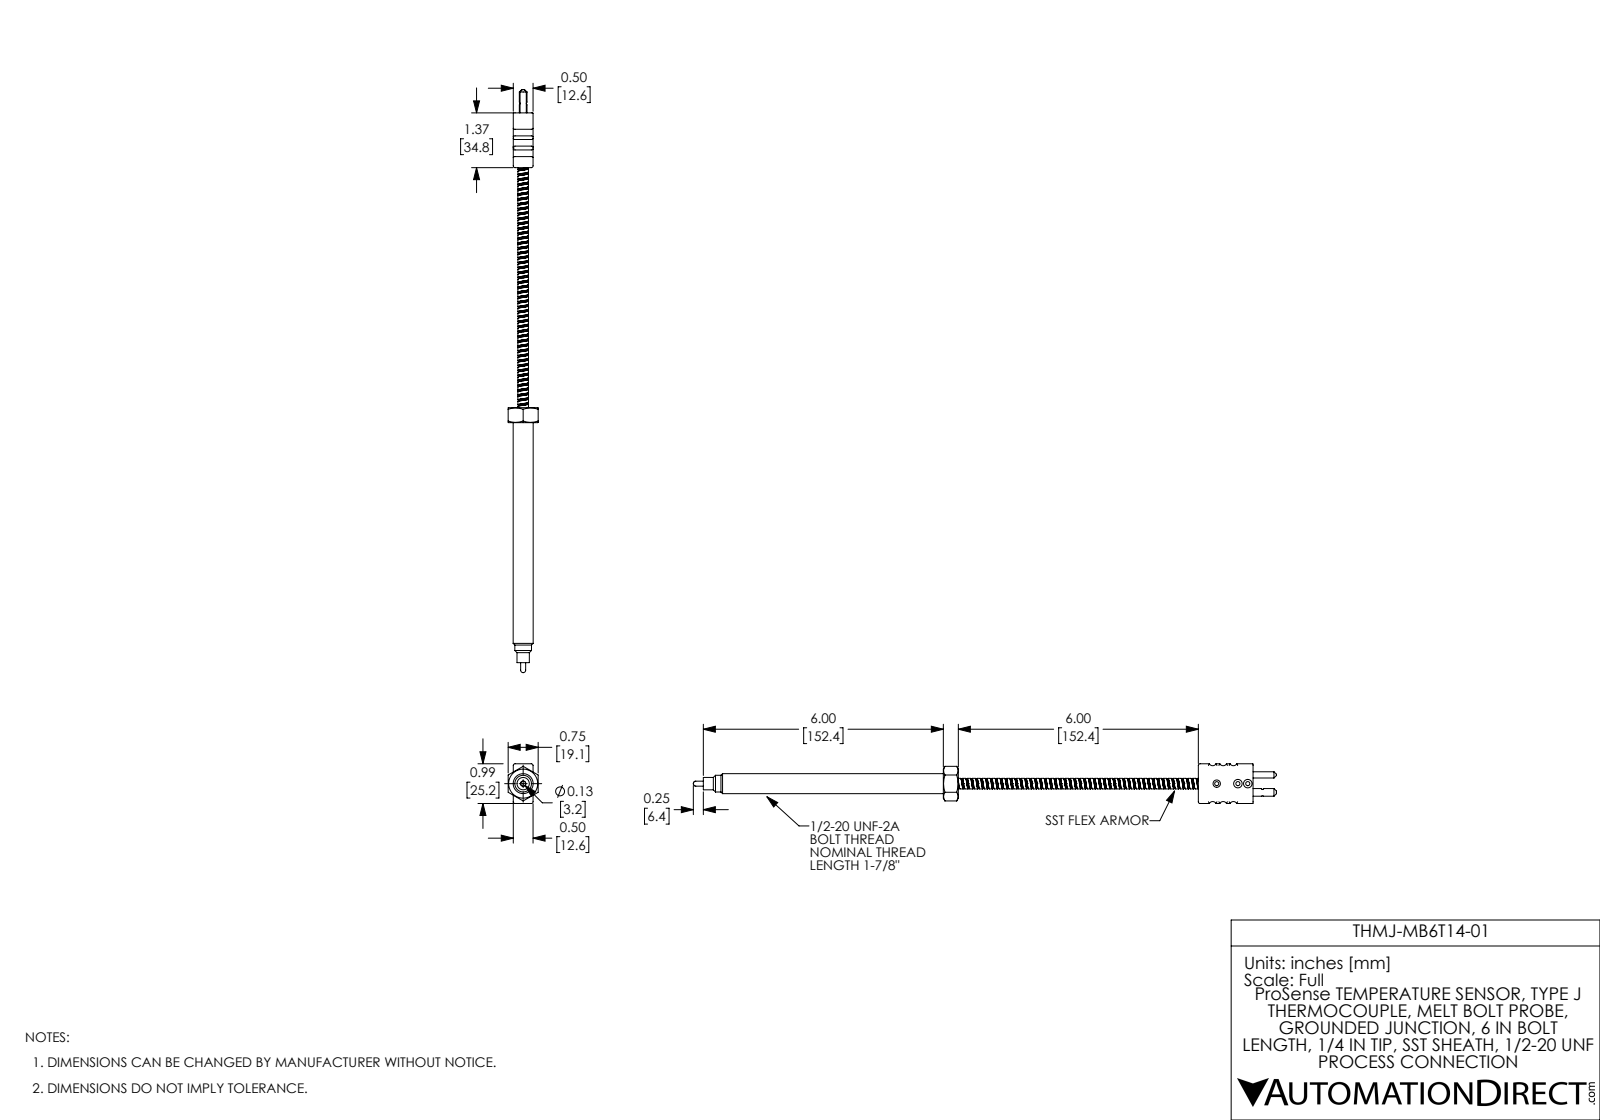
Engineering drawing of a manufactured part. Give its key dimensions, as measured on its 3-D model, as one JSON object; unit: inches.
{"part_name": "THMJ-MB6T14-01", "step_written_by": "SolidWorks 2017 (AUTOMOTIVE_DESIGN)", "units": "inches", "bodies": {"solids": 3, "faces": 312, "planar": 69, "cylindrical": 172, "other": 71}, "overall_size": [14.576, 0.993, 0.75], "volume_in3": 2.274, "surface_area_in2": 23.92, "round_holes": [[0.103, 2], [0.158, 2], [0.135, 1], [0.185, 1], [0.294, 1], [0.308, 1]], "round_bosses_or_shafts": [[0.5, 1], [0.417, 1], [0.309, 1], [0.278, 1], [0.265, 1], [0.191, 1], [0.156, 1], [0.125, 1]], "partial_cylinders_radius": [[0.045, 8], [0.095, 6], [0.01, 4]], "face_to_face_distances": [0.495, 0.75, 7.369, 6, 0.993, 0.127, 0.622, 1.369, 6.375, 7.744], "hole_center_spacings": [0.217, 0.328, 0.572, 0.247, 0.433, 0.529, 0.776]}
